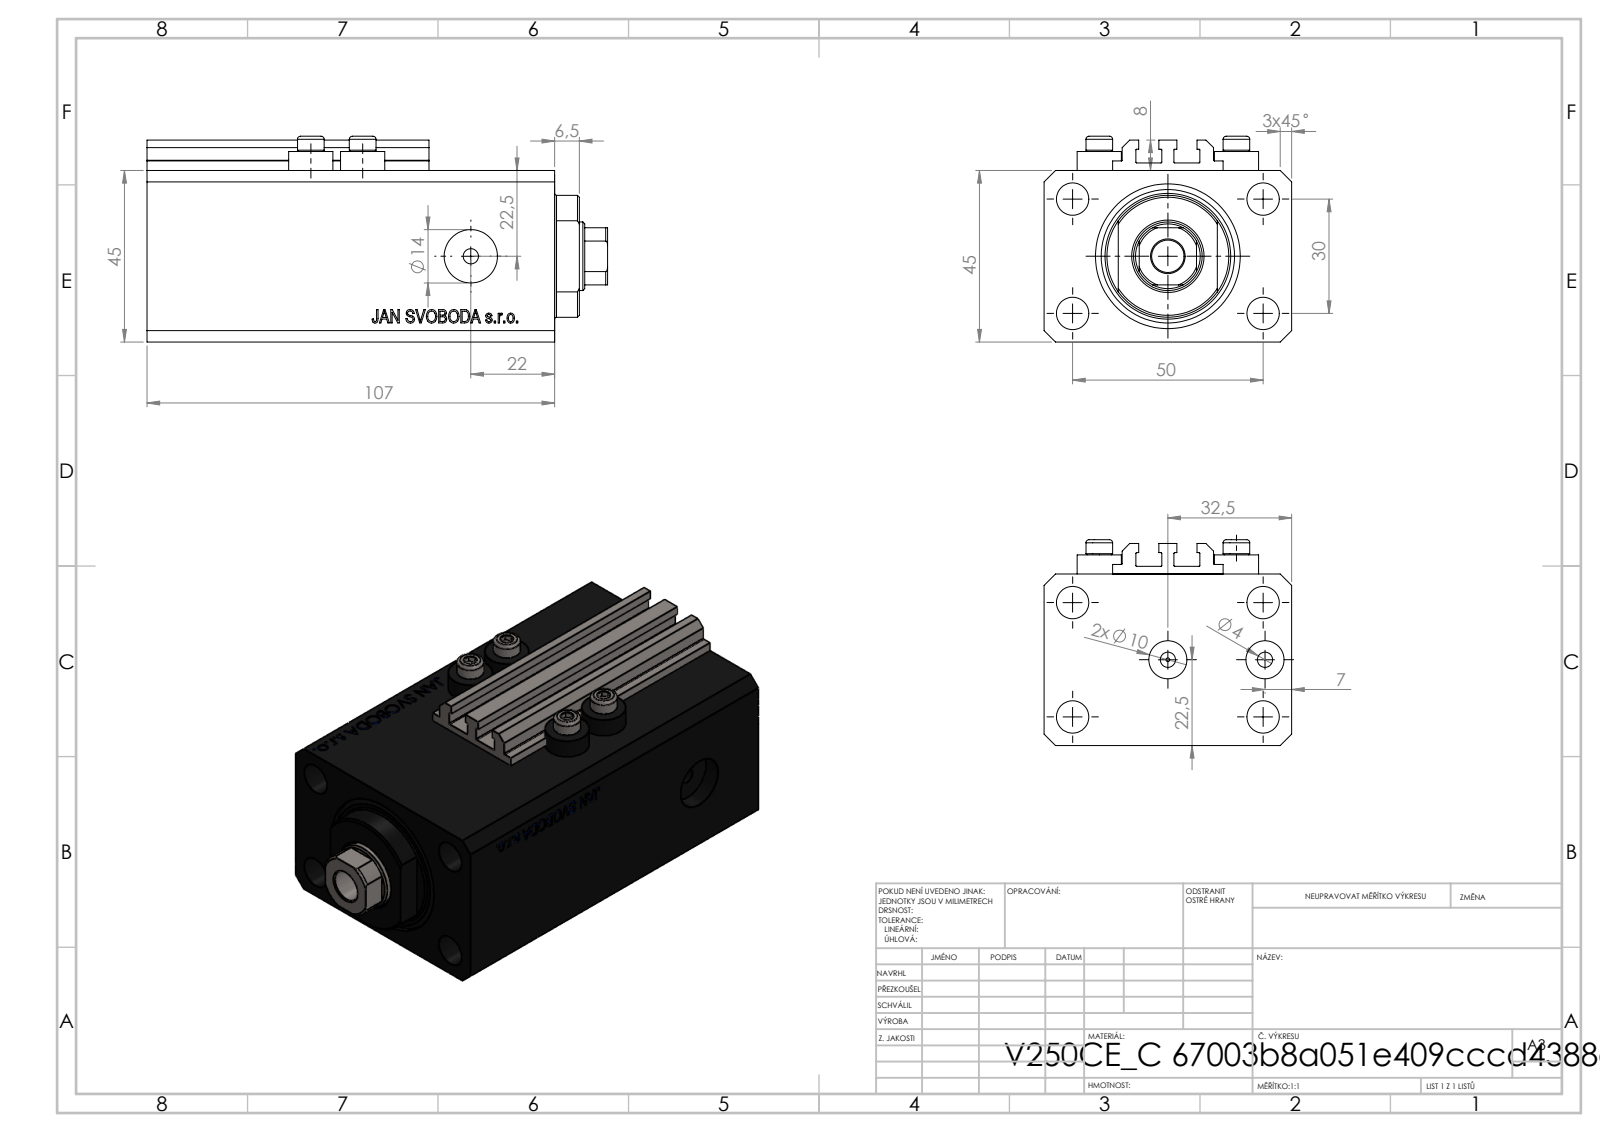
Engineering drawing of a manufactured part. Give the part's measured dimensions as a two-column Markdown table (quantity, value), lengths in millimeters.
| quantity | value |
| --- | --- |
| part name | V250CE_C_VCP; V250CE_C_Body; ALLEN BOLT V250CE; V250CE_VC_C |
| STEP written by | SolidWorks 2019 (CONFIG_CONTROL_DESIGN) |
| units | millimeters |
| bodies | 8 solids, 1038 faces (504 planar, 88 cylindrical, 446 other) |
| overall size | 121 × 65 × 54 |
| volume | 288 552 mm³ |
| surface area | 74 414 mm² |
| round holes (diameter × count) | 4 × 8, 8.5 × 5, 10 × 2, 14 × 2, 1.25 × 1, 18 × 1, 25 × 1, 38 × 1 |
| round bosses / shafts (diameter × count) | 11.6 × 4, 7 × 4 |
| partial cylindrical surfaces (radius × count) | 0.2 × 10, 8.5 × 1, 16 × 1 |
| main face-to-face distances | 45, 65, 14, 107, 93, 47, 2.5, 20.5, 10, 2 |
| hole center spacings | 29.15, 13.6, 15.01, 30, 36, 38.48, 50, 52.68 |
